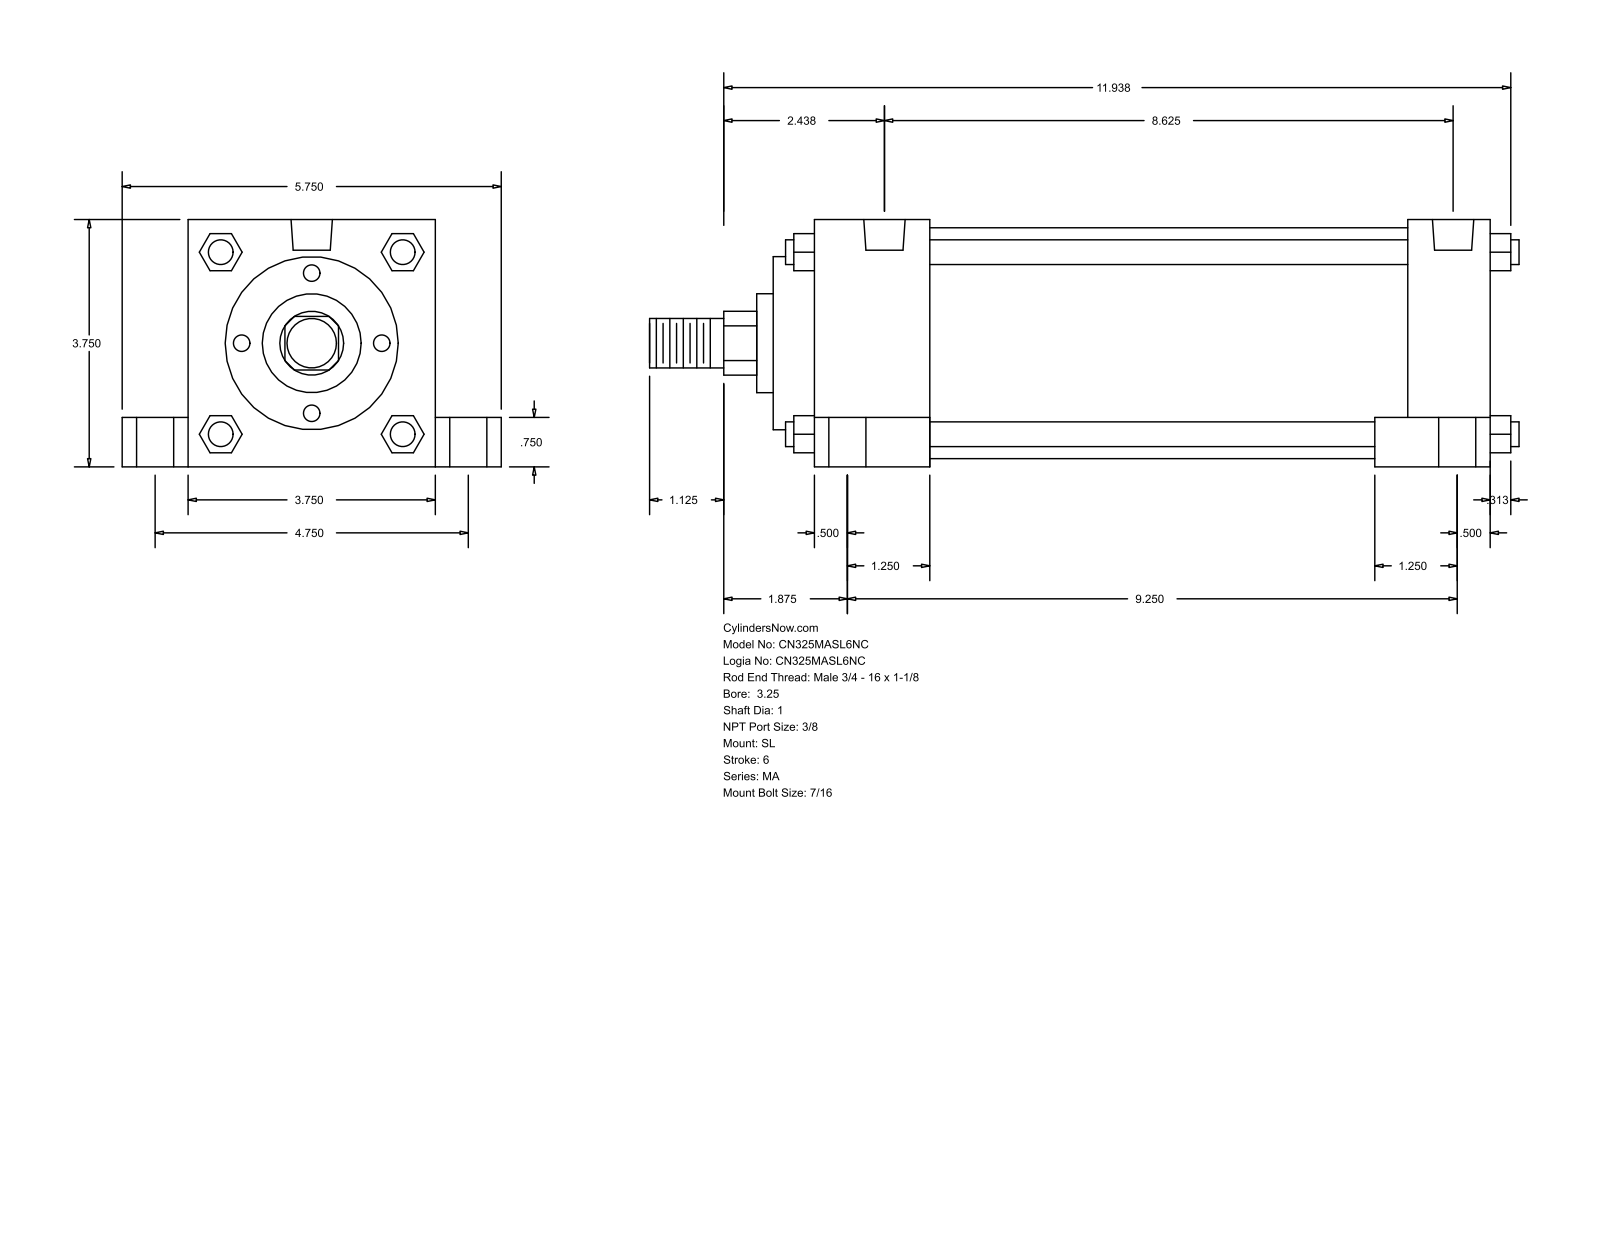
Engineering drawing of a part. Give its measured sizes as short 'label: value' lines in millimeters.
name: MA_SL__0325_1
written by: GSSL Pune (CONFIG_CONTROL_DESIGN)
unit: mm
bodies: 0 solids, 150 faces (113 planar, 37 cylindrical, 0 other)
size: 334.96 × 146.05 × 95.25
holes: 4× ⌀11.11, 4× ⌀14.29, 4× ⌀20.64, 2× ⌀15.93
bosses: 4× ⌀9.53, 1× ⌀88.9, 1× ⌀66.67, 1× ⌀38.1, 1× ⌀25.4, 1× ⌀19.05
rounds: 1× R12.29
face distances: 95.24, 260.35, 15.87, 25.41, 120.65, 276.22, 19.05, 228.6, 31.75, 44.46
hole spacings: 4.76, 60.35, 60.66, 62, 63.27, 120.66, 209.56, 214.32
